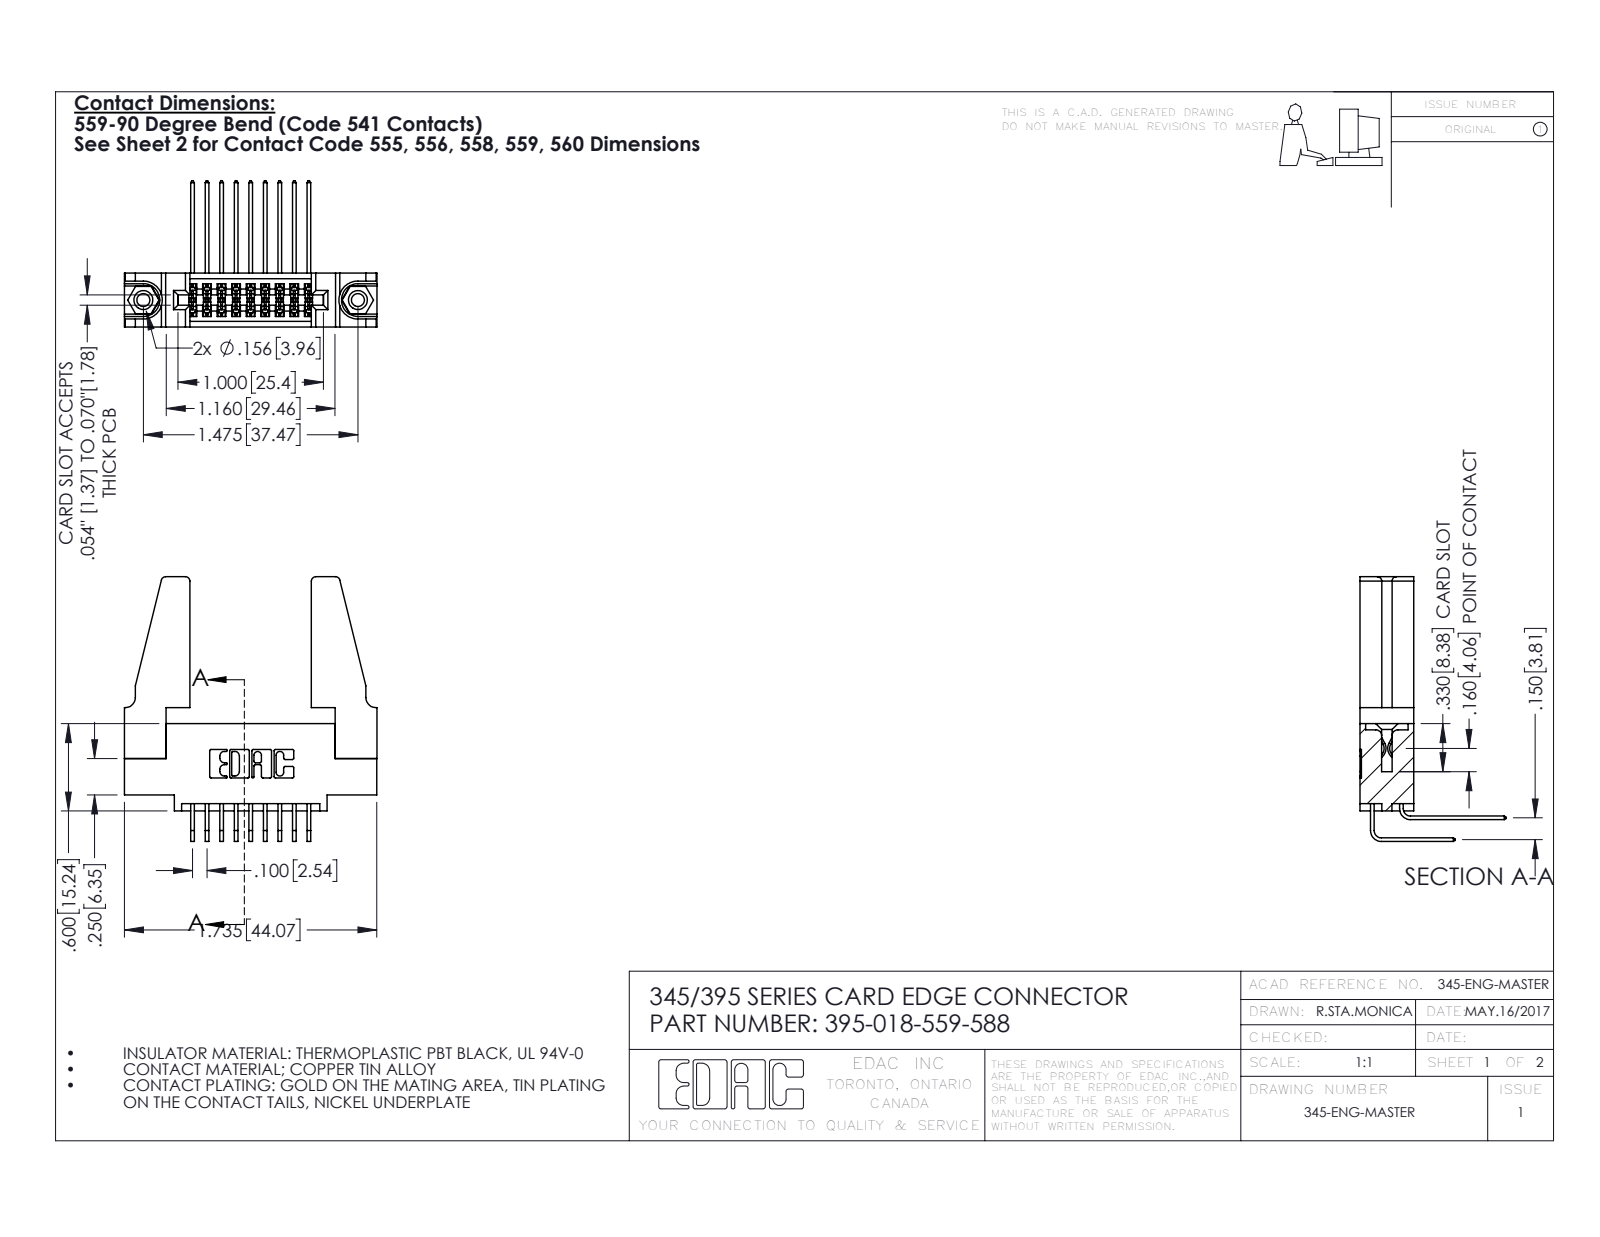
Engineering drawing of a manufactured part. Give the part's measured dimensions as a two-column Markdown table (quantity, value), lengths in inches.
| quantity | value |
| --- | --- |
| part name | 395-018-559-588; 345-250-001_345-250-001-102; 345-292-001_559 Tail - 2; 345-220-078_345-220-088 (+2 more) |
| STEP written by | SolidWorks 2016 (CONFIG_CONTROL_DESIGN) |
| units | inches |
| bodies | 23 solids, 1190 faces (786 planar, 388 cylindrical, 16 other) |
| overall size | 1.819 × 1.736 × 1.005 |
| volume | 0.443 in³ |
| surface area | 13.93 in² |
| round holes (diameter × count) | 0.089 × 2, 0.125 × 2, 0.156 × 2, 0.064 × 1 |
| round bosses / shafts (diameter × count) | 0.155 × 2 |
| partial cylindrical surfaces (radius × count) | 0.006 × 28, 0.01 × 22, 0.03 × 8, 0.007 × 6, 0.031 × 6, 0.026 × 3, 0.014 × 2, 0.019 × 2 |
| main face-to-face distances | 0.37, 0.072, 0.298, 0.2, 0.098, 0.272, 0.025, 0.225, 0.15, 0.15 |
| hole center spacings | 0.27, 1.244, 1.475 |
